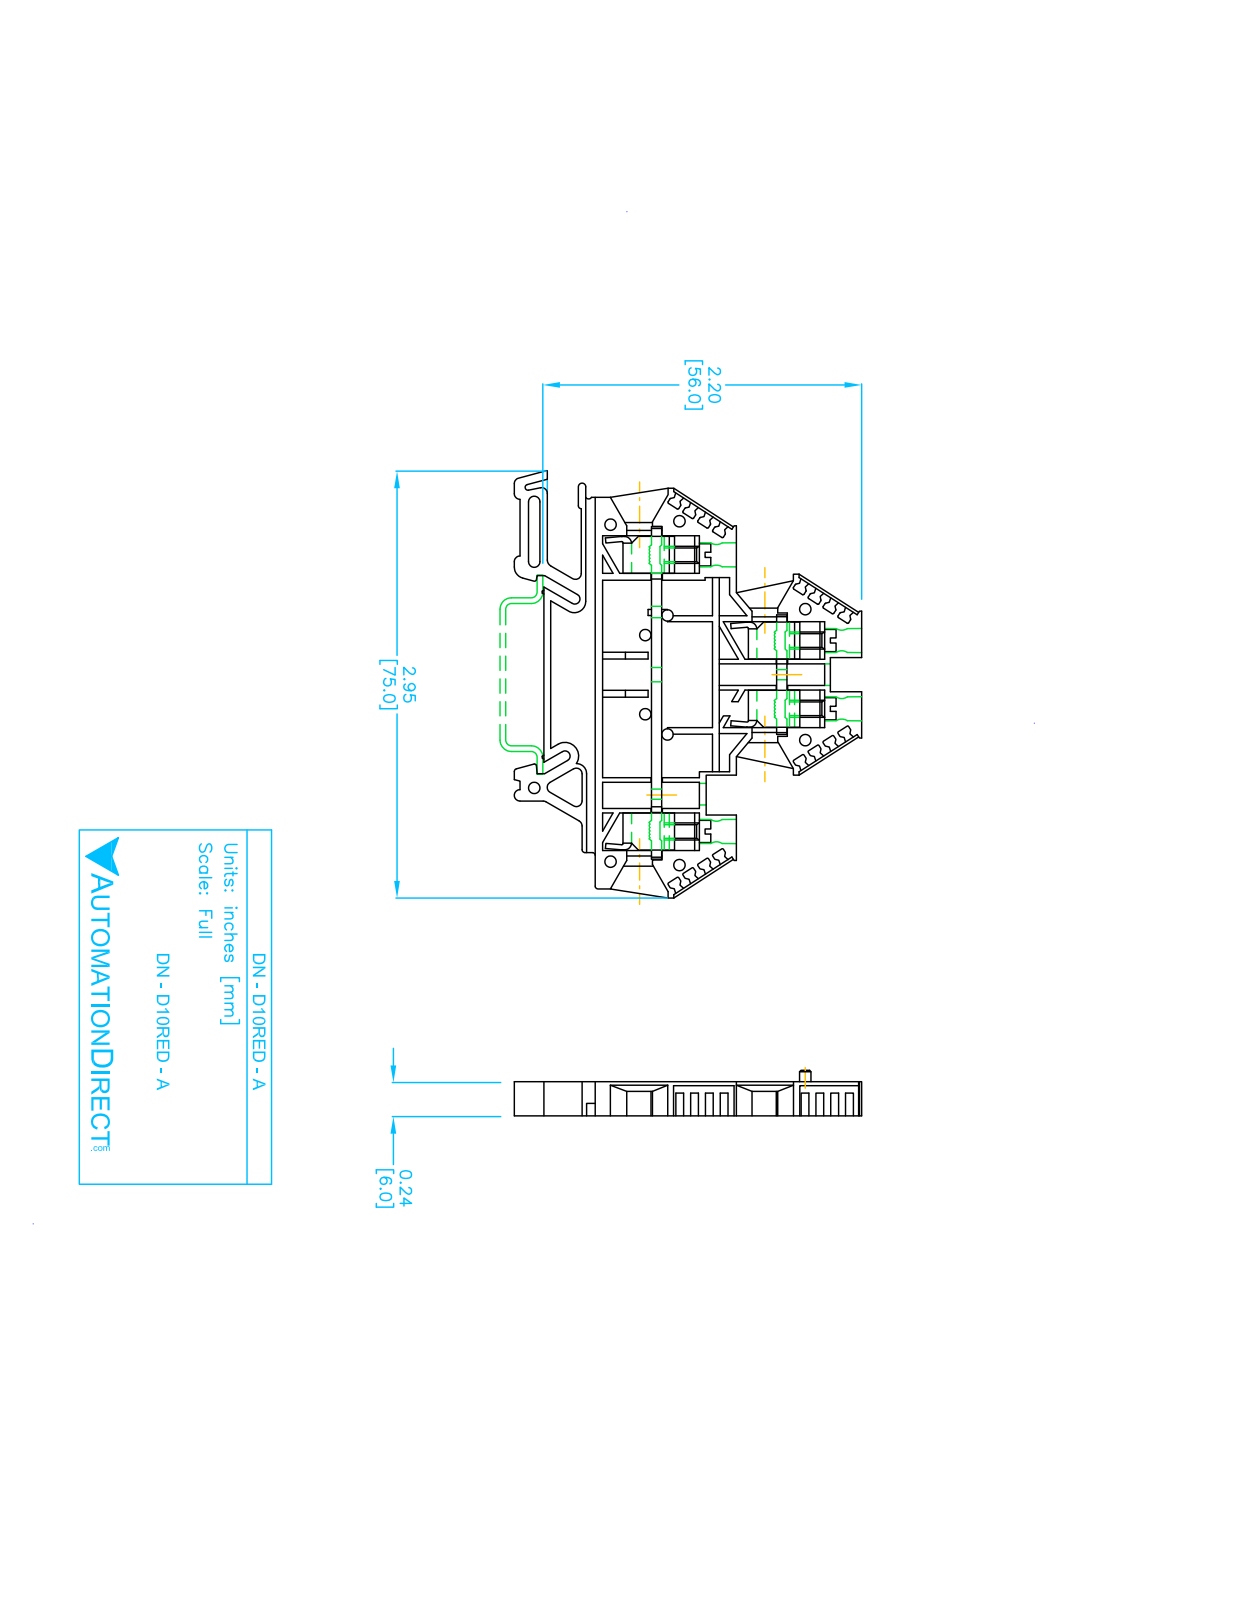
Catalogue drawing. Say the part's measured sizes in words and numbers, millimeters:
The part is named "DN-D10RED-A". Its 3-D file was written by "SolidWorks 2017 (AUTOMOTIVE_DESIGN)". It is 1 solid with 402 faces: 261 planar, 141 cylindrical and 0 other. Overall it measures 75.1 by 61 by 6 millimeters. Its volume is 14 700 cubic millimeters and its surface area 9 581 square millimeters. Round holes: 4 of diameter 4.2, 1 of diameter 2. Round bosses or shafts: 4 of diameter 3.7. Partial cylindrical surfaces (rounded edges, fillets, slot ends): 64 of radius 0.2, 13 of radius 1, 6 of radius 0.5, 2 of radius 0.3, 2 of radius 0.9, 2 of radius 1.9, 2 of radius 2, 1 of radius 0.1. The main face-to-face distances are 6, 2, 4, 9, 1.5, 0.6, 0.8, 1.2, 24.8, 1.8. The hole center spacings are 12, 15.1, 21.5, 27.1, 33.6, 48.6.
